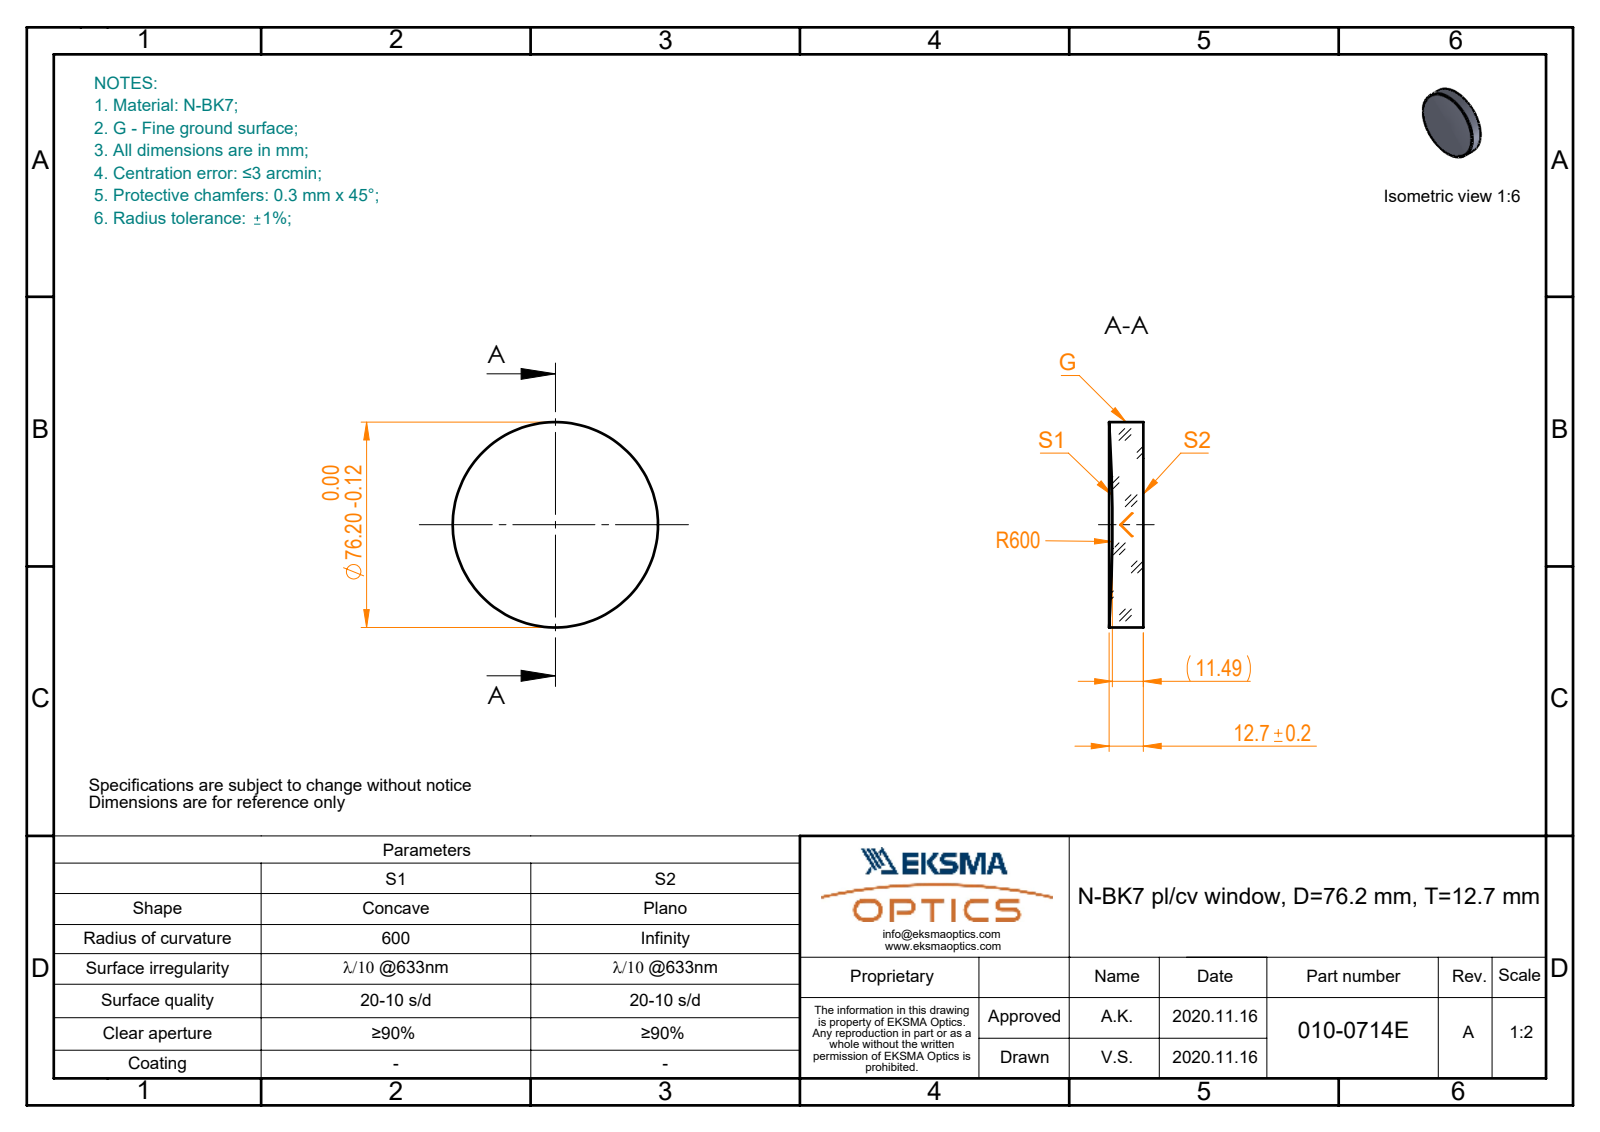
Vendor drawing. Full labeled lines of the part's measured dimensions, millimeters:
Part name (STEP PRODUCT): 010-0714E_N-BK7_PCV_window
STEP written by: SolidWorks 2019 (CONFIG_CONTROL_DESIGN)
Units: millimetres
Bodies: 1 solid, 5 faces (1 planar, 2 cylindrical, 2 other)
Overall size (bounding box): 76.2 × 76.2 × 12.7
Volume: 55 155 mm³ · Surface area: 12 166 mm²
Round bosses / shafts (diameter × count): ⌀76.2 ×1
